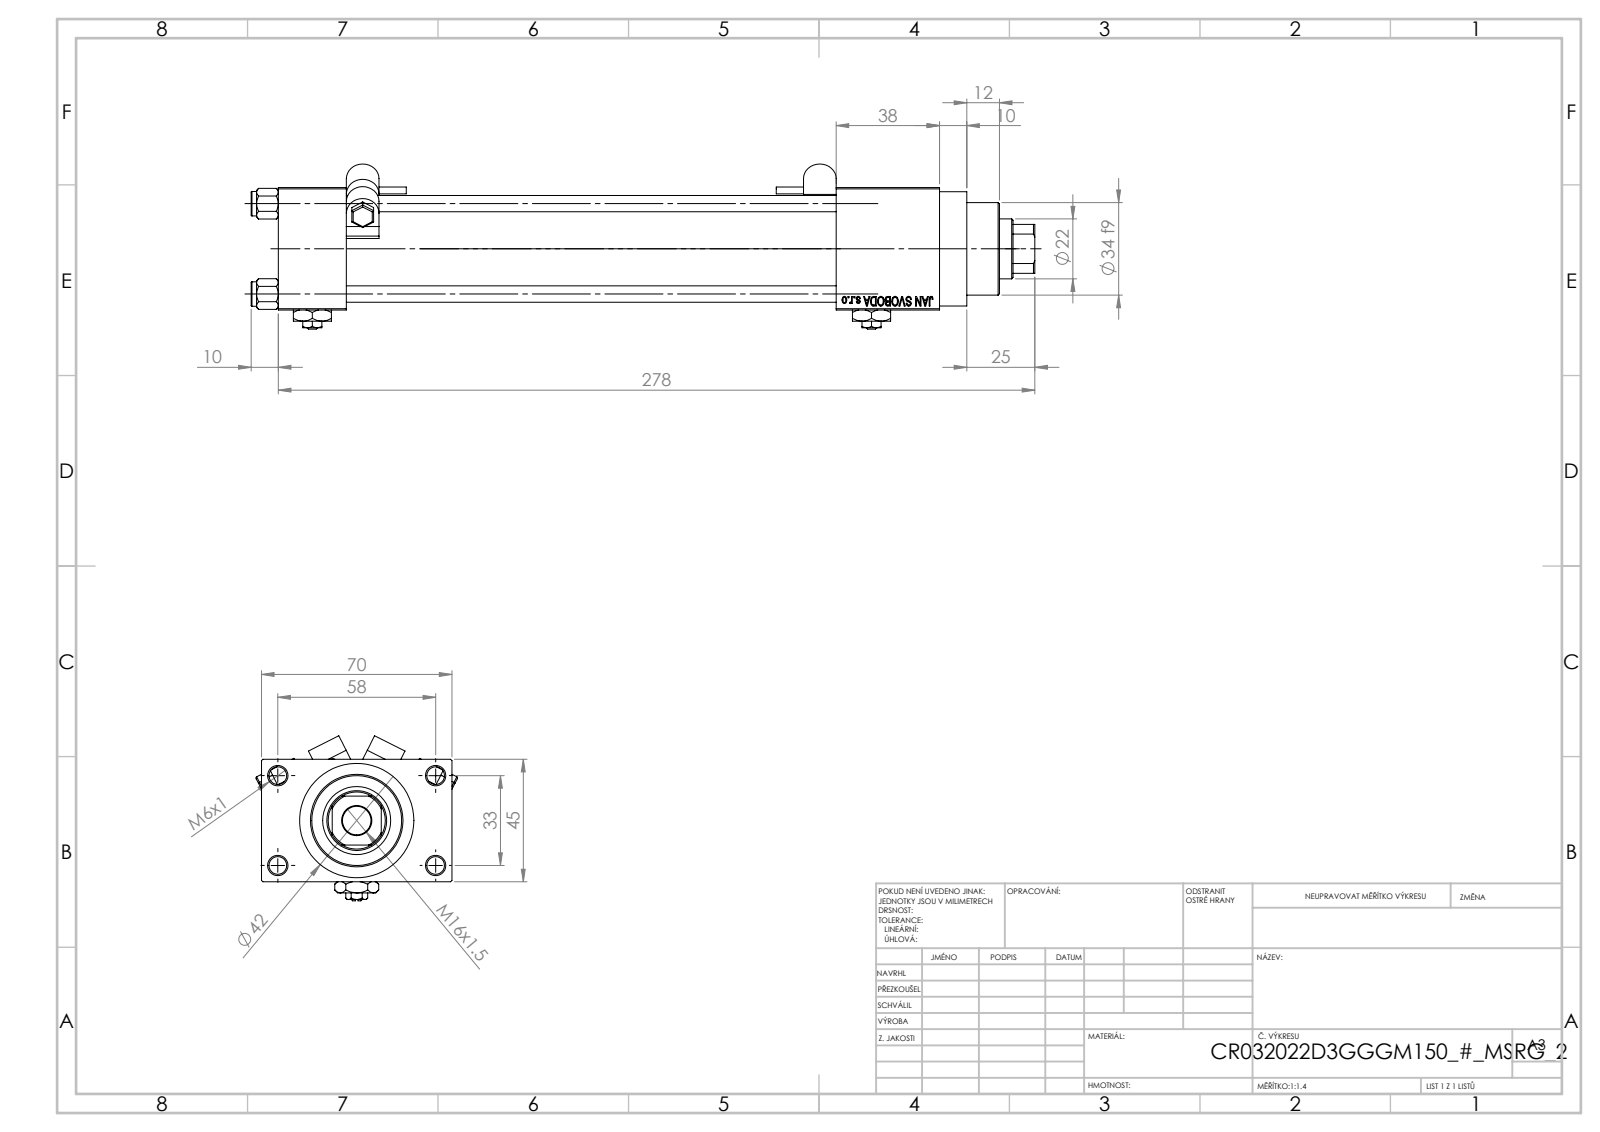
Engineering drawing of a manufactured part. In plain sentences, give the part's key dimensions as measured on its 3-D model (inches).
The part is named "V215CR_D_TYCINKA; NUT_M5_D; V215CR_D_Body; Zatka_pro_OIL_PORT (+3 more)". Its 3-D file was written by "SolidWorks 2019 (CONFIG_CONTROL_DESIGN)". It is 15 solids with 1266 faces: 578 planar, 128 cylindrical and 560 other. Overall it measures 11.339 by 2.915 by 2.388 inches. Its volume is 21.81 cubic inches and its surface area 205.8 square inches. Round holes: 4 of diameter 0.236, 4 of diameter 0.256, 2 of diameter 0.276, 2 of diameter 0.518, 2 of diameter 0.787, 1 of diameter 0.413, 1 of diameter 0.866, 1 of diameter 0.945, 1 of diameter 0.984, 1 of diameter 1.26, 1 of diameter 1.299. Round bosses or shafts: 4 of diameter 0.354, 2 of diameter 0.197, 2 of diameter 0.098, 1 of diameter 1.654, 1 of diameter 1.496, 1 of diameter 1.339. Partial cylindrical surfaces (rounded edges, fillets, slot ends): 12 of radius 0.02, 4 of radius 0.236, 1 of radius 0.413. The main face-to-face distances are 1.772, 0.984, 0.492, 2.264, 7.087, 8.071, 8.583, 1.496, 2.756, 9.567. The hole center spacings are 0.488, 0.924, 1.307, 1.314, 1.392, 1.795, 2.219, 1.299.
